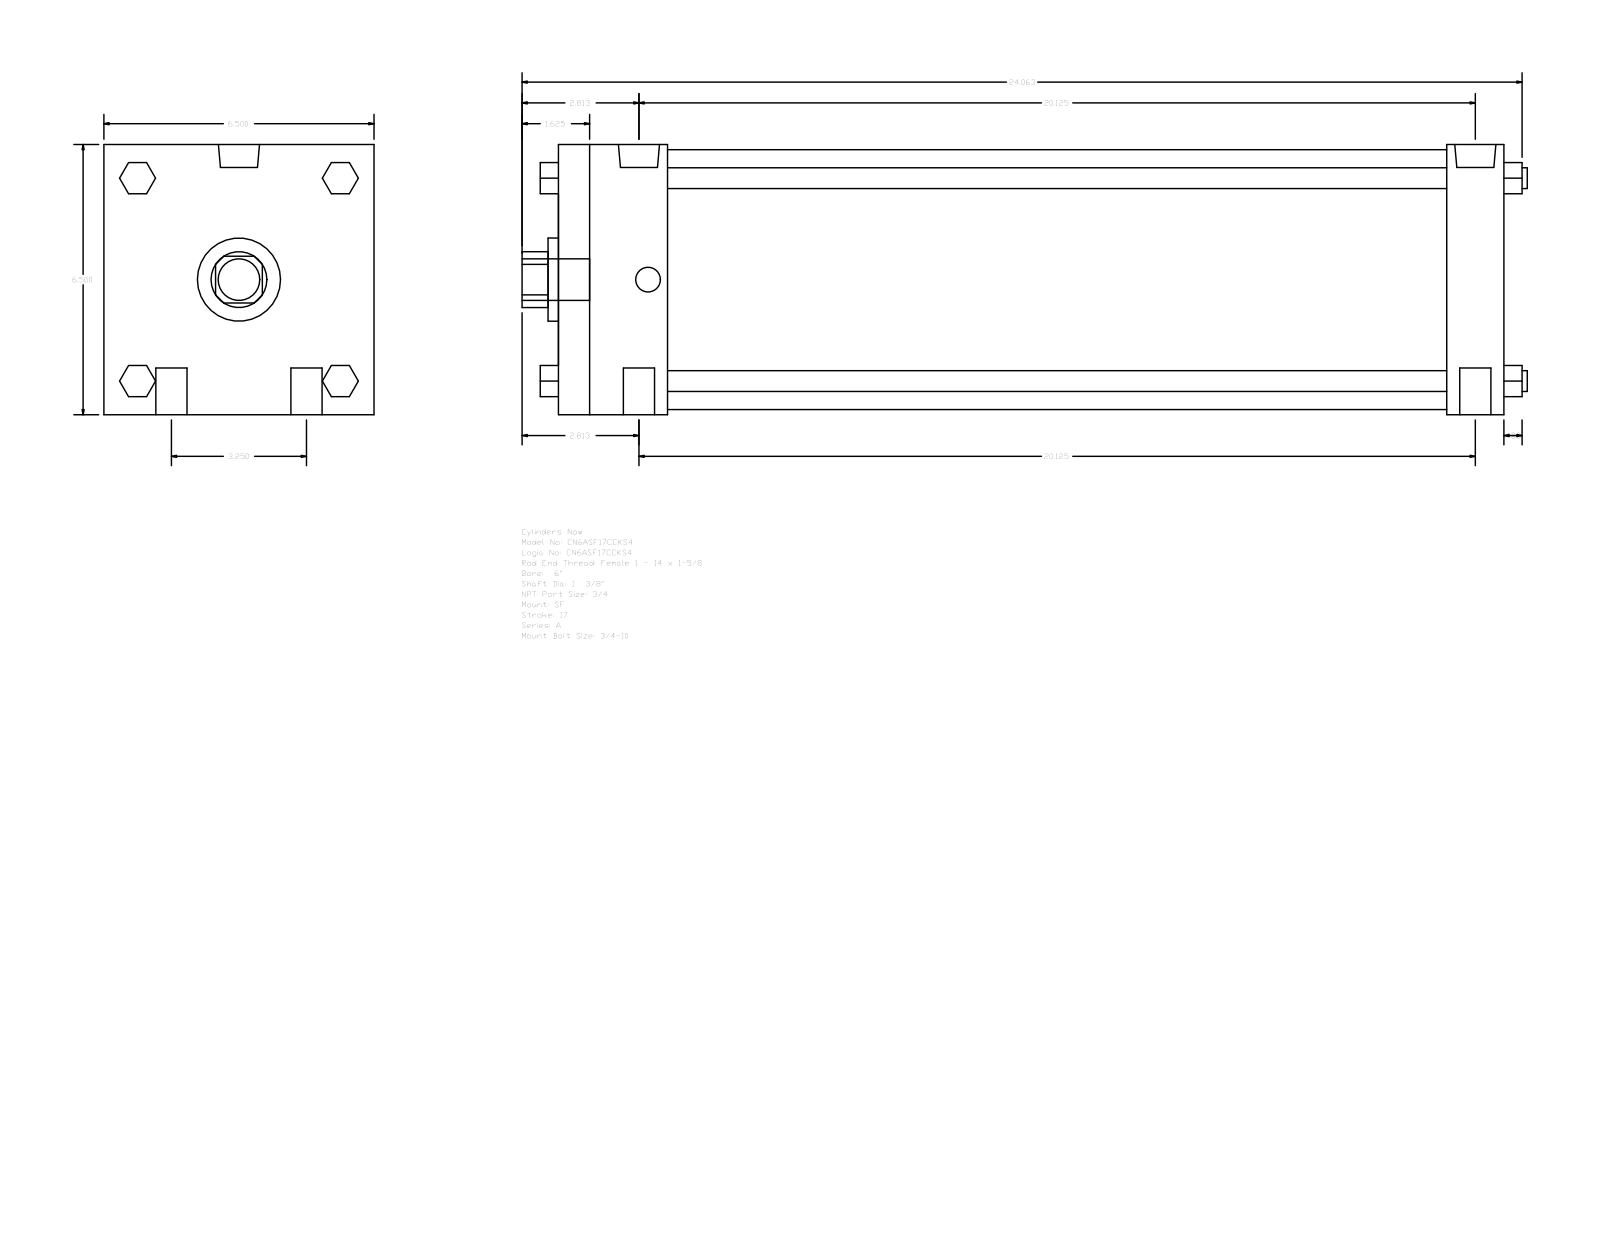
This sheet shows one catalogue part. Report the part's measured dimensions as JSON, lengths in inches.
{"part_name": "A_SF__0600_1.375", "step_written_by": "GSSL Pune (CONFIG_CONTROL_DESIGN)", "units": "inches", "bodies": {"solids": 0, "faces": 124, "planar": 94, "cylindrical": 30, "other": 0}, "overall_size": [24.187, 6.5, 6.5], "round_holes": [[1.375, 1], [2, 1], [6.25, 1]], "round_bosses_or_shafts": [[0.75, 4], [0.5, 4], [0.989, 2], [0.594, 2], [1, 1]], "partial_cylinders_radius": [[0.672, 1]], "face_to_face_distances": [6.5, 22.75, 21.375, 1.375, 2.625, 18.75, 20.125, 0.75, 2.44, 4.226]}
